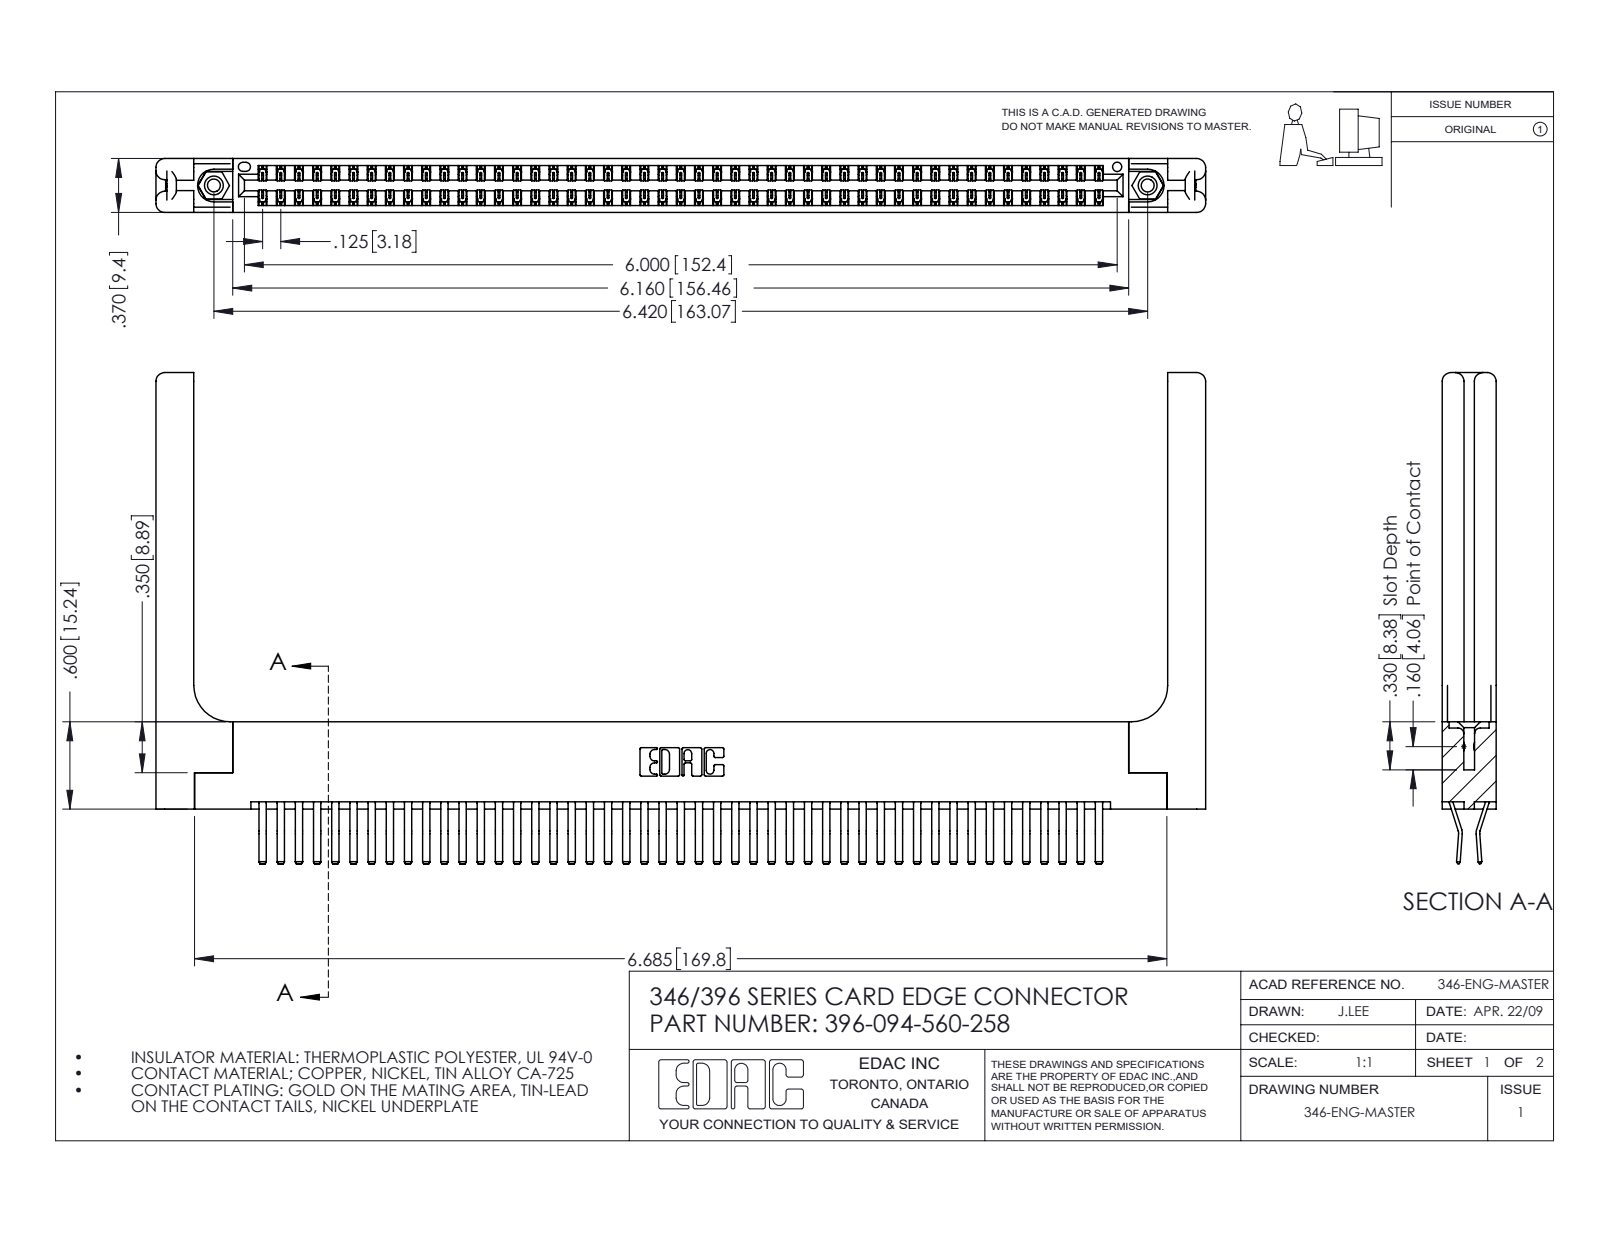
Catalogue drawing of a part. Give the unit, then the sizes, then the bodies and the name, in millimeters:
Units: millimetres
Overall size (bounding box): 183.3 × 85.7 × 9.4
Round holes (diameter × count): ⌀2.3 ×2, ⌀3.2 ×2, ⌀4 ×2, ⌀1.6 ×1
Round bosses / shafts (diameter × count): ⌀3.9 ×2
Partial cylindrical surfaces — rounded edges, fillets, slot ends (radius × count): R0.2 ×141, R0.3 ×22, R1.5 ×16, R0.2 ×6, R0.8 ×6, R0.7 ×3, R0.3 ×2, R0.4 ×2
Main face-to-face distances: 9.4, 1.2, 8.2, 1.8, 0.6, 3.8, 3.8, 6.4, 7.6, 7
Hole centre spacings: 6.2, 157.8, 163.1
Volume: 26 020 mm³ · Surface area: 32 160 mm²
Bodies: 99 solids, 5454 faces (3514 planar, 1880 cylindrical, 60 other)
Part name (STEP PRODUCT): 346-220-058_345-220-058; 396-094-560-258; 345-250-001_345-250-001-102; 345-292-001_560 Tail (+1 more)
STEP written by: SolidWorks 2016 (CONFIG_CONTROL_DESIGN)
